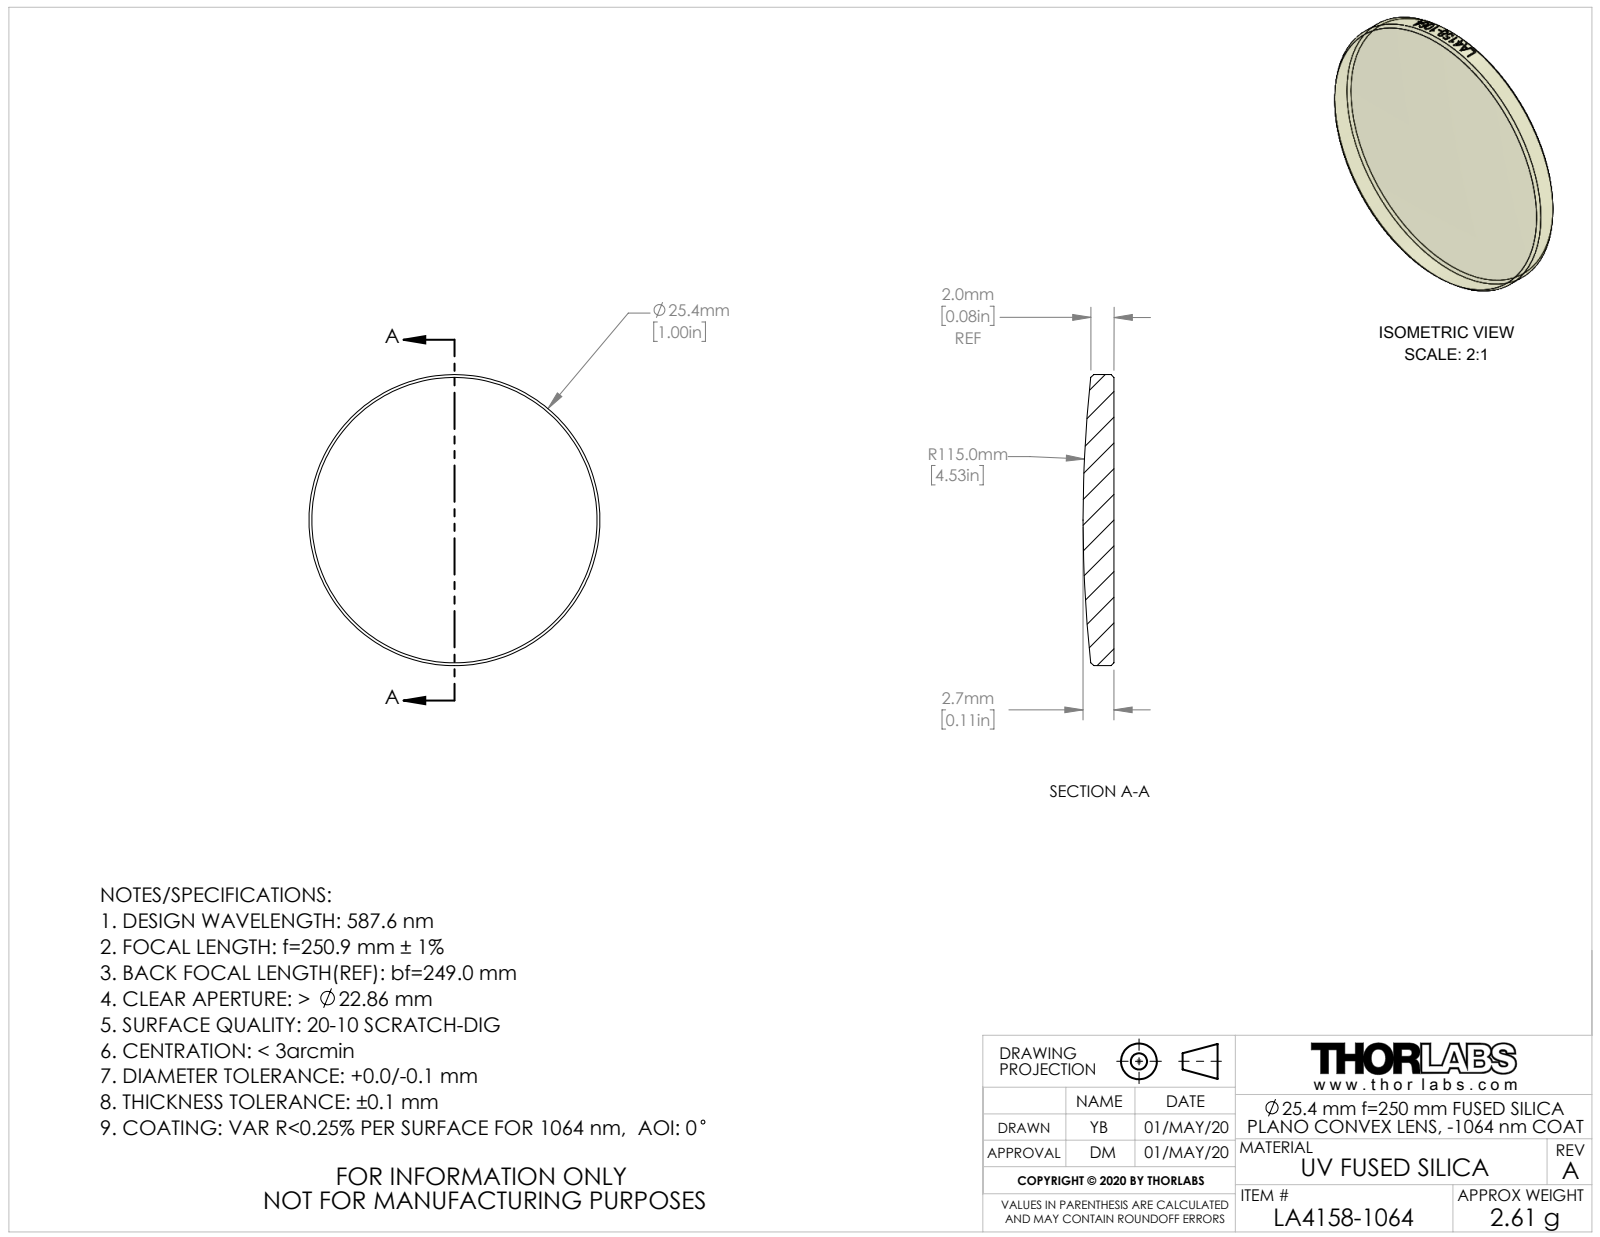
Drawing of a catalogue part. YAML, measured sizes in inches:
part_name: "CTN015548-E0W"
step_written_by: "SolidWorks 2018 (AUTOMOTIVE_DESIGN)"
units: inches
bodies: {solids: 1, faces: 30, planar: 1, cylindrical: 23, other: 6}
overall_size: [1, 1, 0.106]
volume: 0.072
surface_area: 1.787
round_bosses_or_shafts:
  - {diameter: 1, count: 1}
